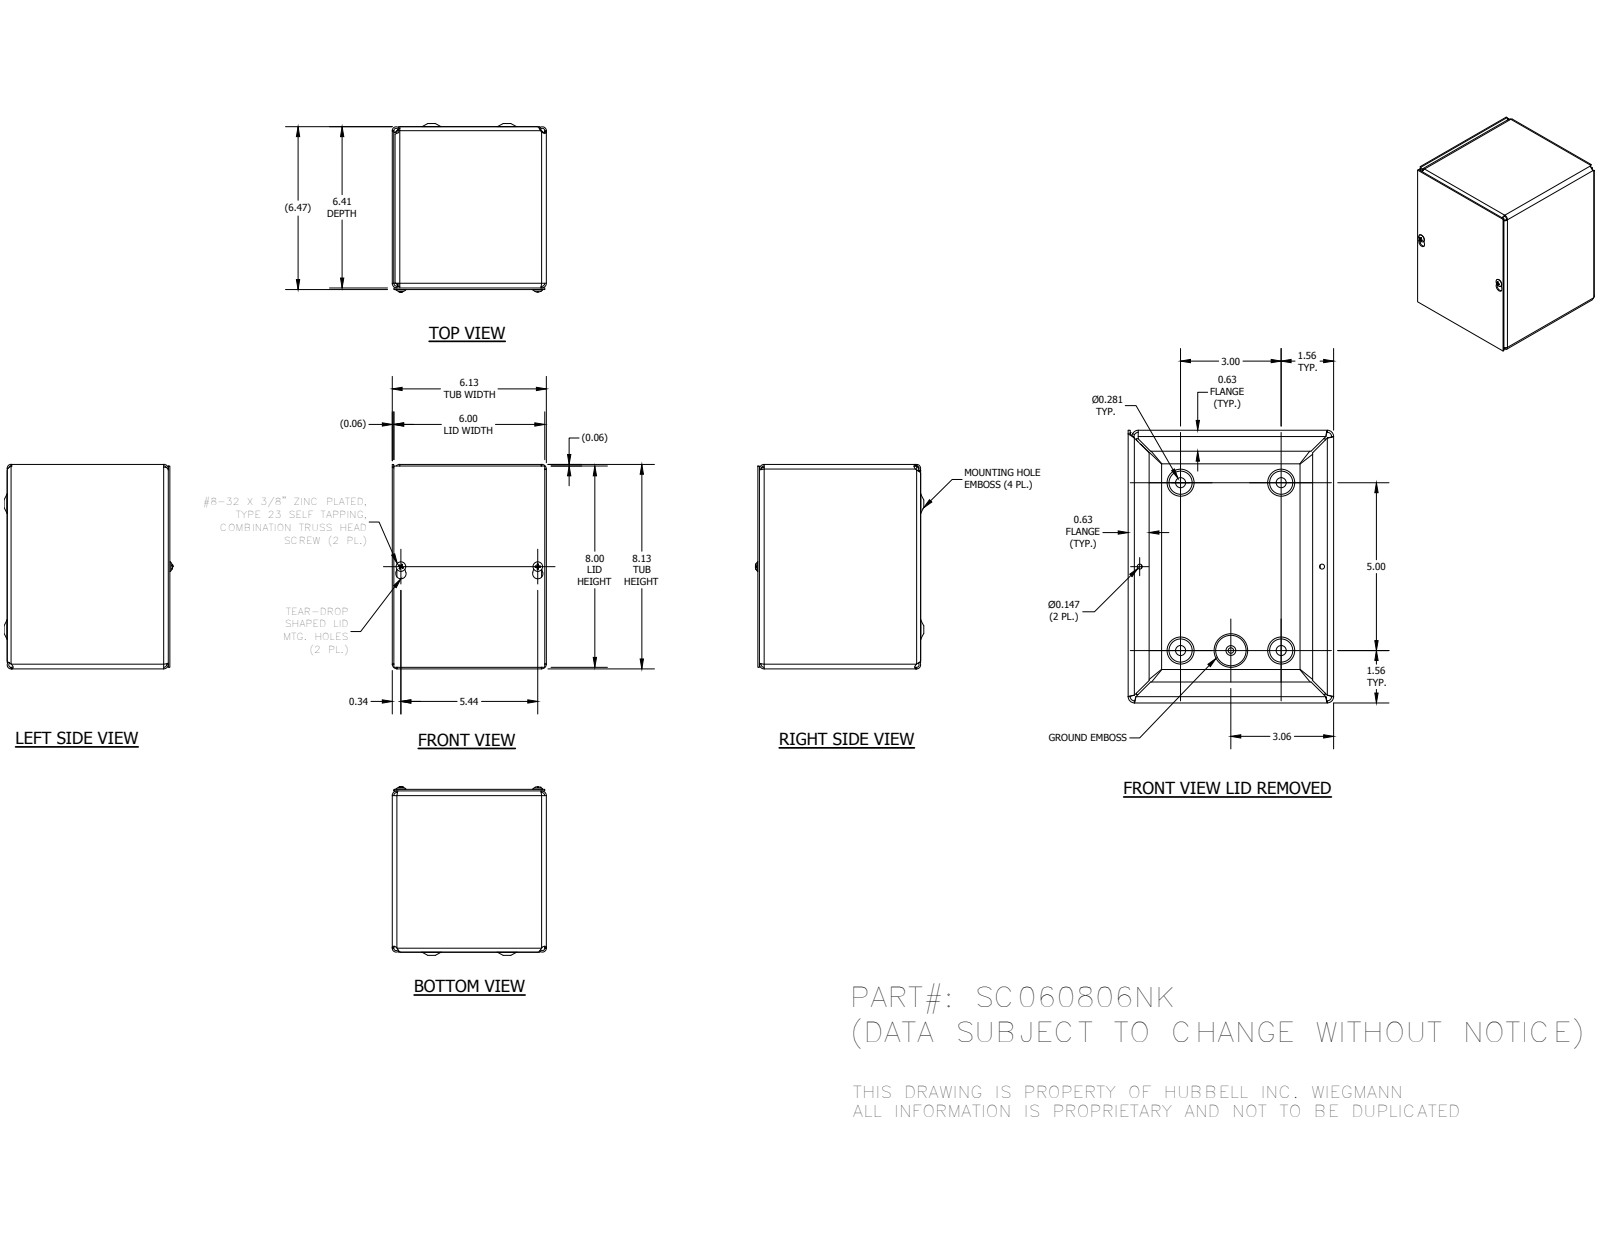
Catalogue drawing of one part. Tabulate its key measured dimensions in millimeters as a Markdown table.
| quantity | value |
| --- | --- |
| part name | SC0608BKP; SC060806NKWRA; SC0608LID; 34056 (+1 more) |
| STEP written by | Autodesk Inventor 2014 (AUTOMOTIVE_DESIGN) |
| units | millimeters |
| bodies | 5 solids, 293 faces (108 planar, 57 cylindrical, 128 other) |
| overall size | 206.38 × 170 × 155.57 |
| volume | 311 852 mm³ |
| surface area | 401 638 mm² |
| round holes (diameter × count) | 7.62 × 4, 3.73 × 2, 4.19 × 1 |
| round bosses / shafts (diameter × count) | 9.75 × 2, 4.17 × 2, 5.8 × 1 |
| partial cylindrical surfaces (radius × count) | 3.17 × 10, 4.75 × 8, 1.4 × 4, 1.57 × 4, 2.38 × 4, 2.97 × 4, 3.15 × 4, 3.96 × 4 |
| main face-to-face distances | 1.57, 1.58, 161.12, 162.69, 154, 155.58, 152.43, 154.01, 1.59, 162.71 |
| hole center spacings | 38.1, 70.64, 70.65, 76.2, 124.55, 124.56, 127, 132.59 |
